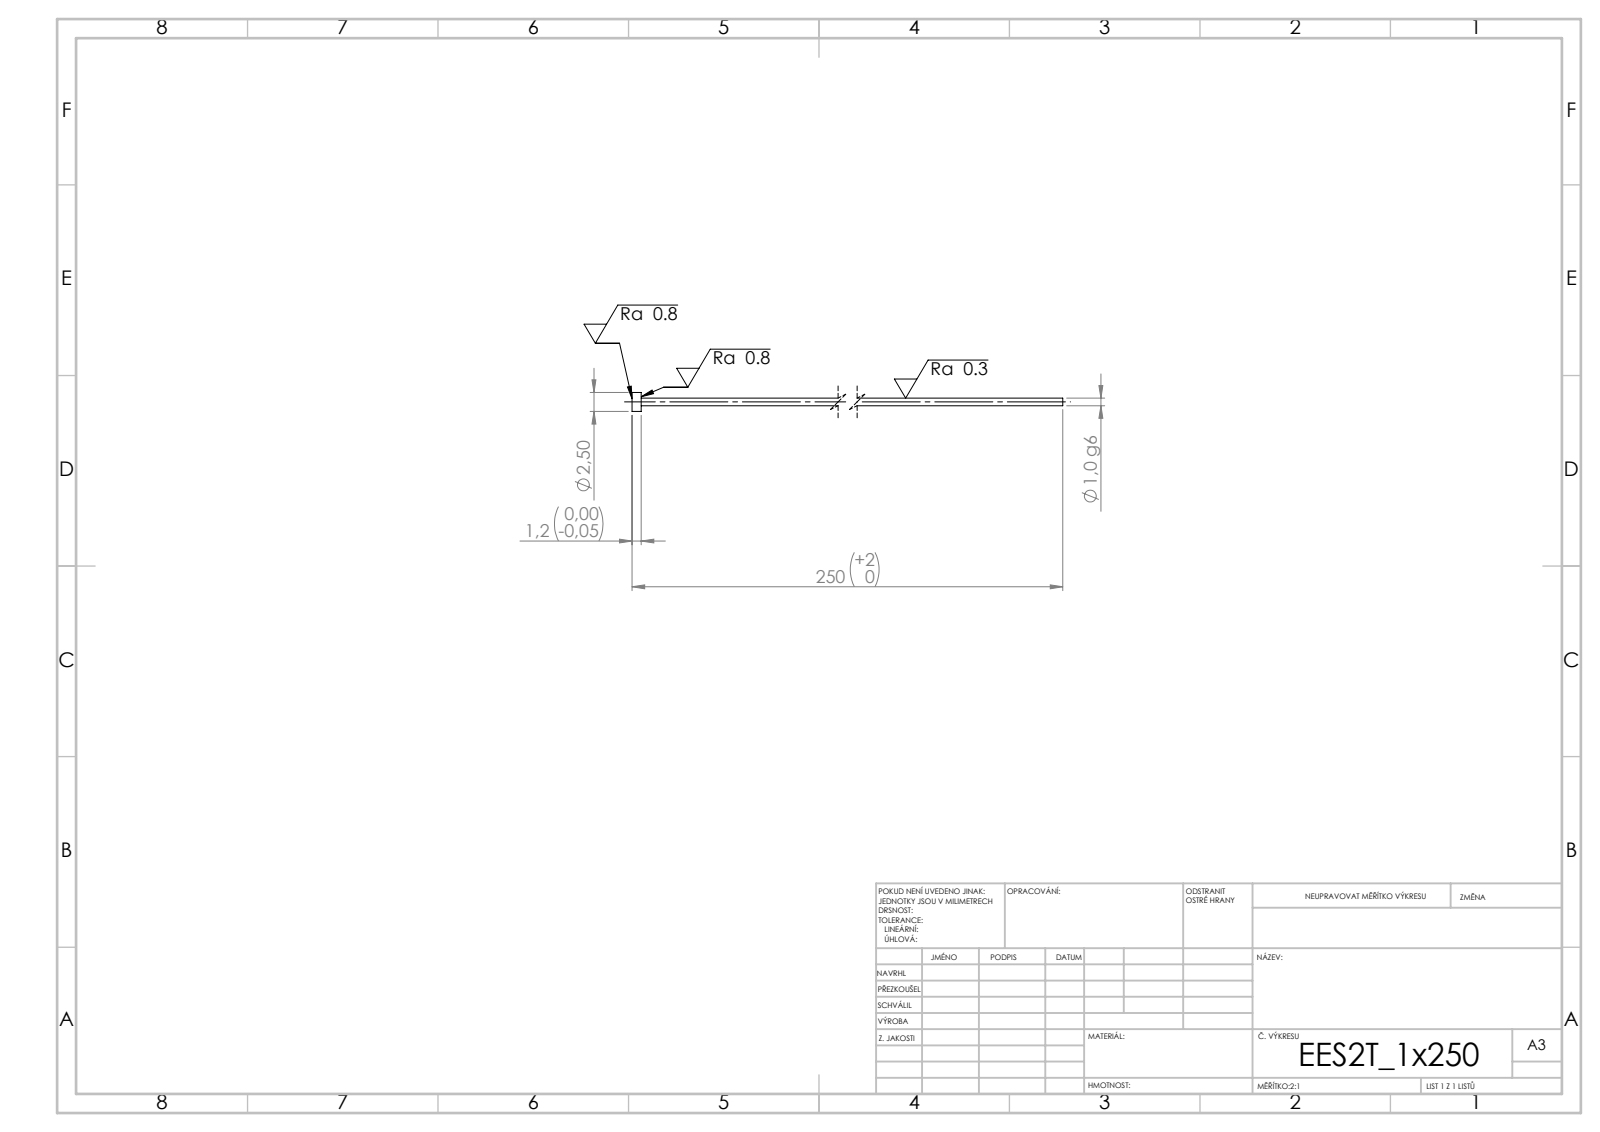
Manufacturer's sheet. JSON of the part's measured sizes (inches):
{"step_written_by": "SolidWorks 2019 (CONFIG_CONTROL_DESIGN)", "units": "inches", "bodies": {"solids": 1, "faces": 7, "planar": 3, "cylindrical": 4, "other": 0}, "overall_size": [9.843, 0.098, 0.098], "volume_in3": 0.012, "surface_area_in2": 1.24, "round_bosses_or_shafts": [[0.098, 1], [0.039, 1]], "face_to_face_distances": [0.047, 9.843, 9.795]}
